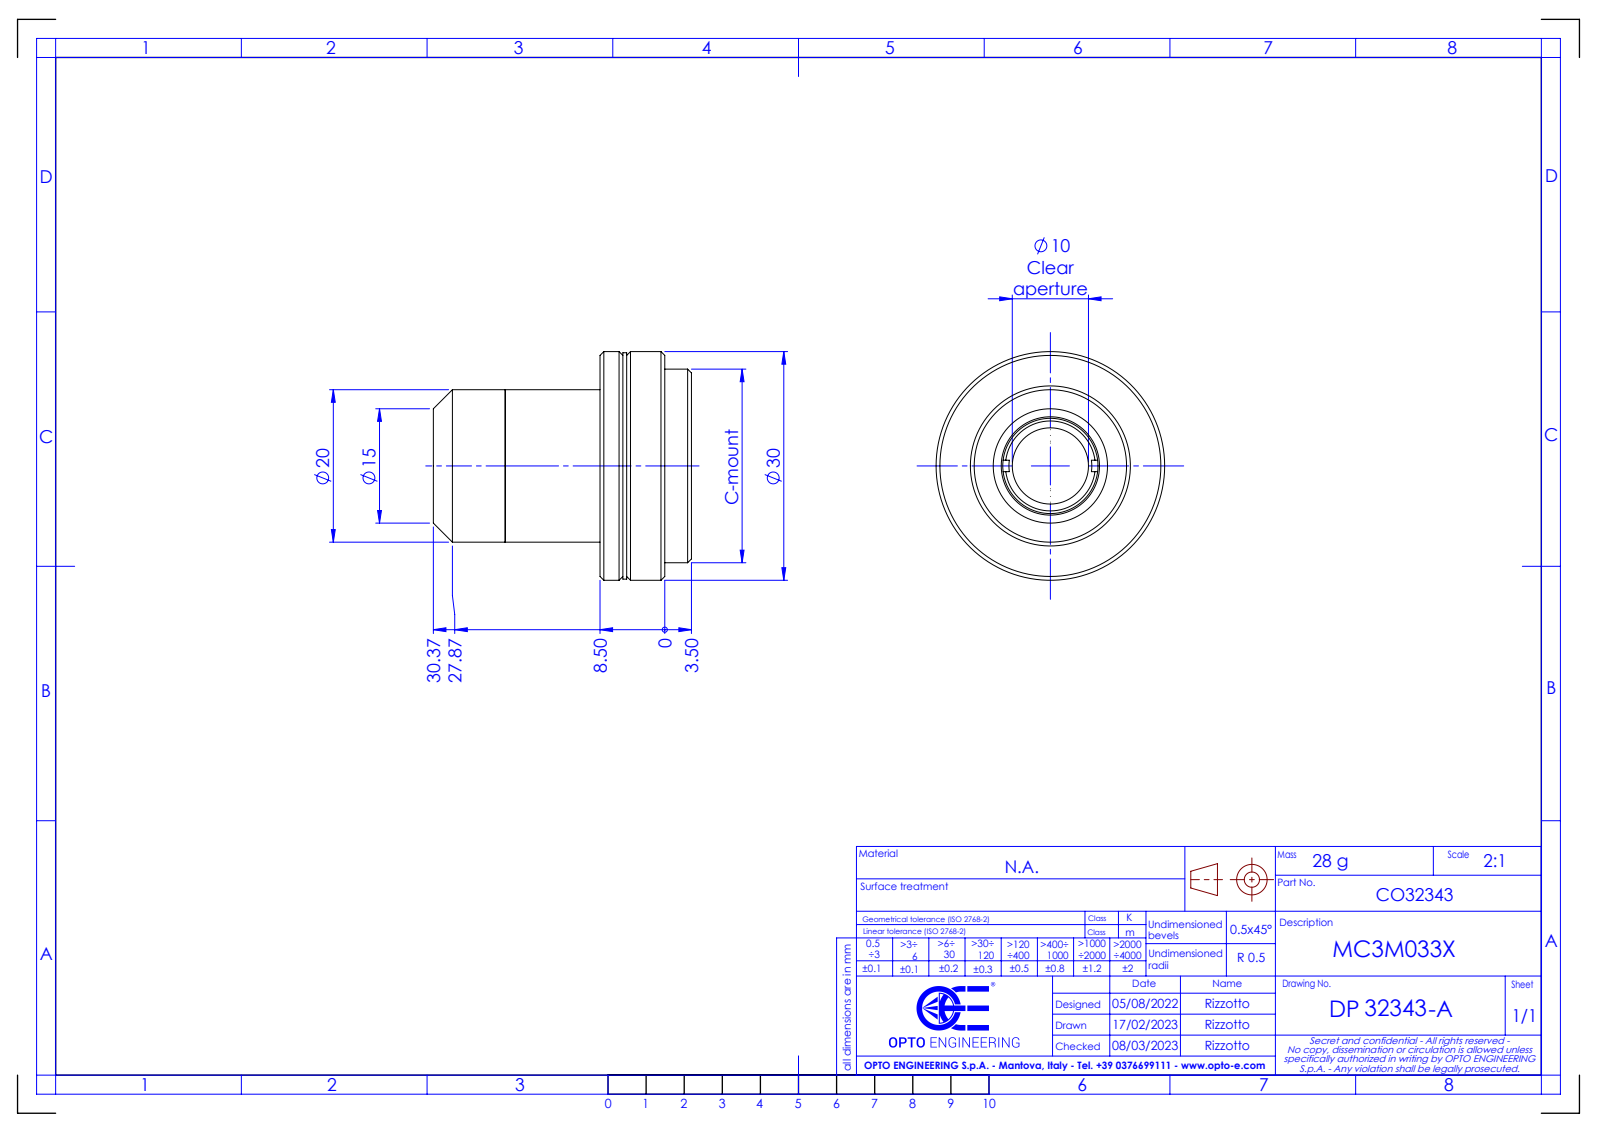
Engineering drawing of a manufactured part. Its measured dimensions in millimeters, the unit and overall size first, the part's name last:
Units: millimetres
Overall size (bounding box): 33.88 × 30 × 30
Round holes (diameter × count): ⌀10 ×1, ⌀12.5 ×1, ⌀15.5 ×1, ⌀18 ×1
Round bosses / shafts (diameter × count): ⌀30 ×1, ⌀29.7 ×1, ⌀25.4 ×1, ⌀20 ×1
Main face-to-face distances: 8.5, 3.5, 5, 3, 0.5, 5.5, 12, 9, 7.8, 4.8
Bodies: 0 solids, 65 faces (17 planar, 22 cylindrical, 26 other)
Part name (STEP PRODUCT): DP32343-A_MC3M033X
STEP written by: SolidWorks 2021 (CONFIG_CONTROL_DESIGN)
